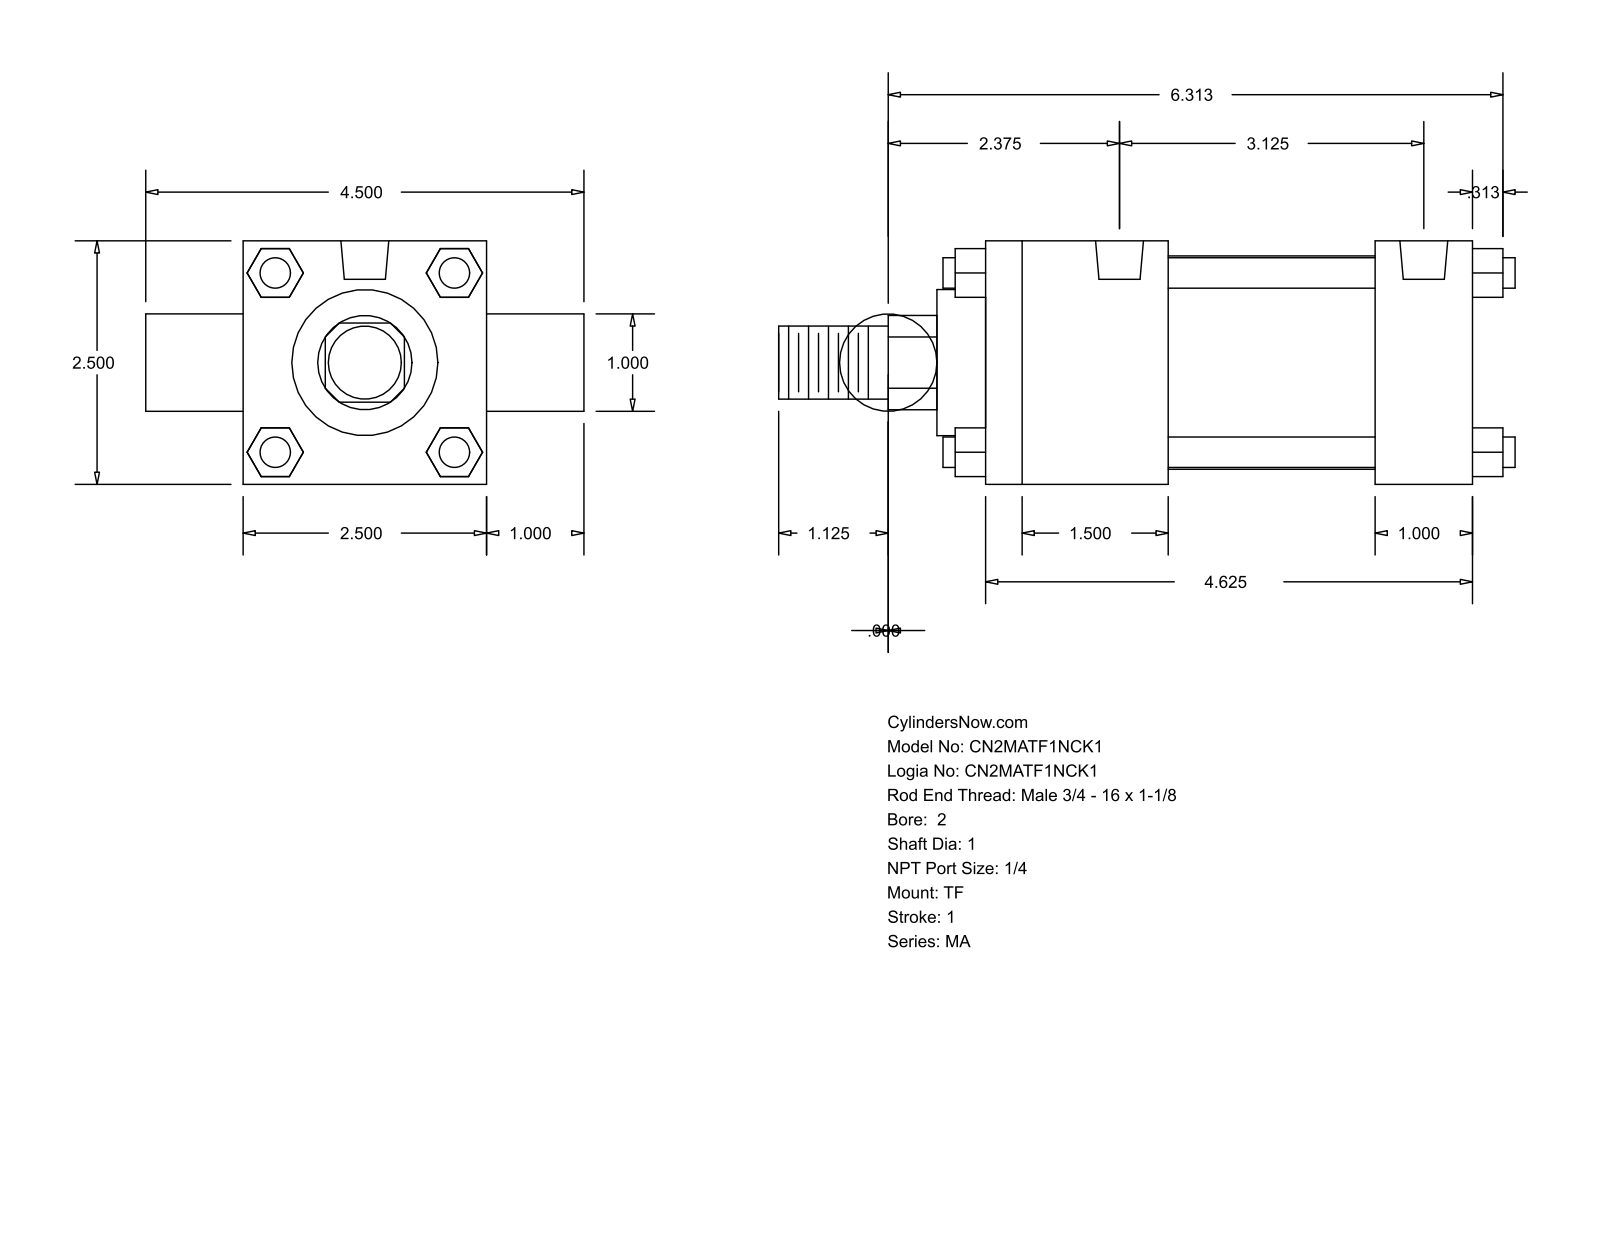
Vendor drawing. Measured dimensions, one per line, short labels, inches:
name: MA_TF__0200_1
written by: GSSL Pune (CONFIG_CONTROL_DESIGN)
unit: in
bodies: 0 solids, 120 faces (92 planar, 28 cylindrical, 0 other)
size: 7.563 × 4.5 × 2.5
holes: 3× ⌀0.313, 2× ⌀0.492
bosses: 4× ⌀0.313, 2× ⌀1, 1× ⌀2.19, 1× ⌀1.5, 1× ⌀0.75
rounds: 1× R0.484
face distances: 2.5, 1, 5, 0.5, 2.125, 4, 1.875, 3.125, 4.5, 3.5
hole spacings: 3.125
